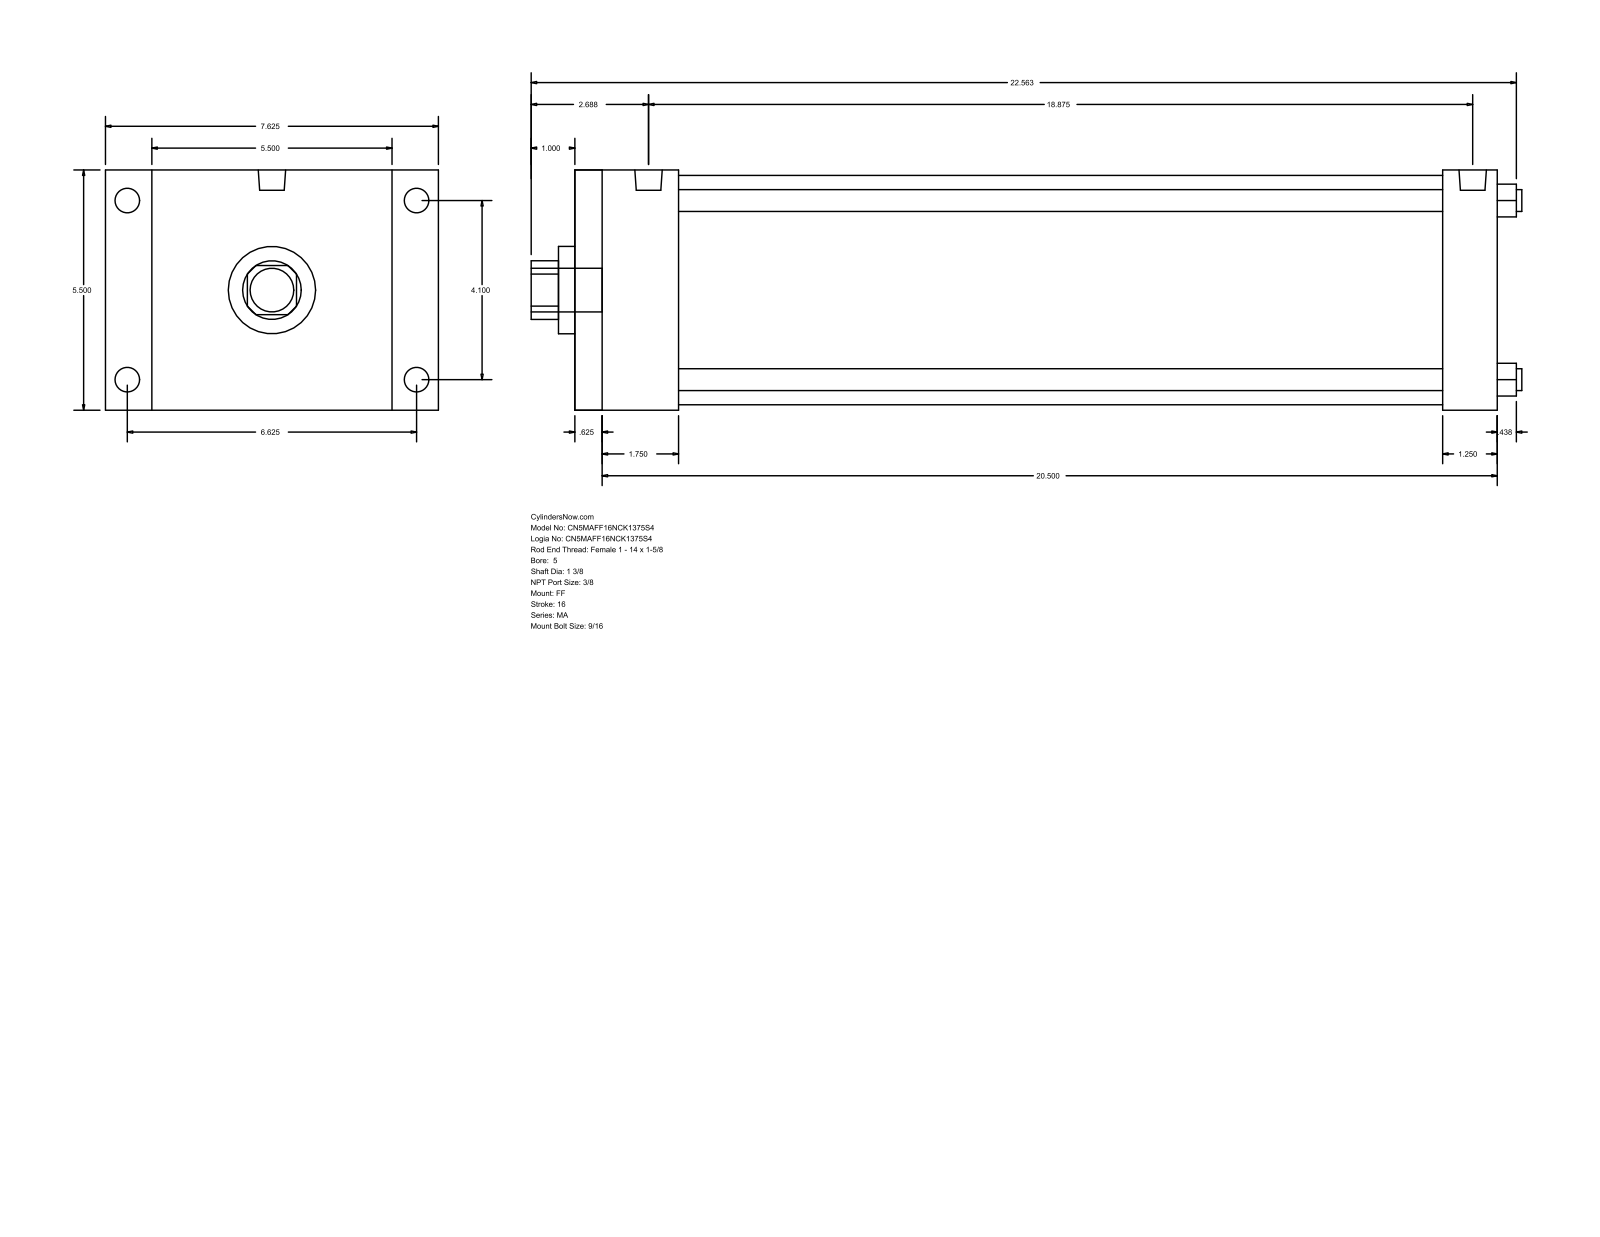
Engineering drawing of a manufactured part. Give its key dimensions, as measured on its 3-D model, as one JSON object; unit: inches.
{"part_name": "MA_FF__0500_1.375", "step_written_by": "GSSL Pune (CONFIG_CONTROL_DESIGN)", "units": "inches", "bodies": {"solids": 0, "faces": 92, "planar": 64, "cylindrical": 28, "other": 0}, "overall_size": [22.687, 7.625, 5.5], "round_holes": [[0.5, 4], [1.375, 1], [2, 1], [5.25, 1]], "round_bosses_or_shafts": [[0.563, 4], [0.437, 4], [0.627, 2], [1, 1]], "partial_cylinders_radius": [[0.672, 1]], "face_to_face_distances": [5.5, 21.125, 0.625, 20.5, 19.875, 19.25, 1.25, 2.375, 1.75, 17.5], "hole_center_spacings": [2.899, 4.1, 5.798]}
